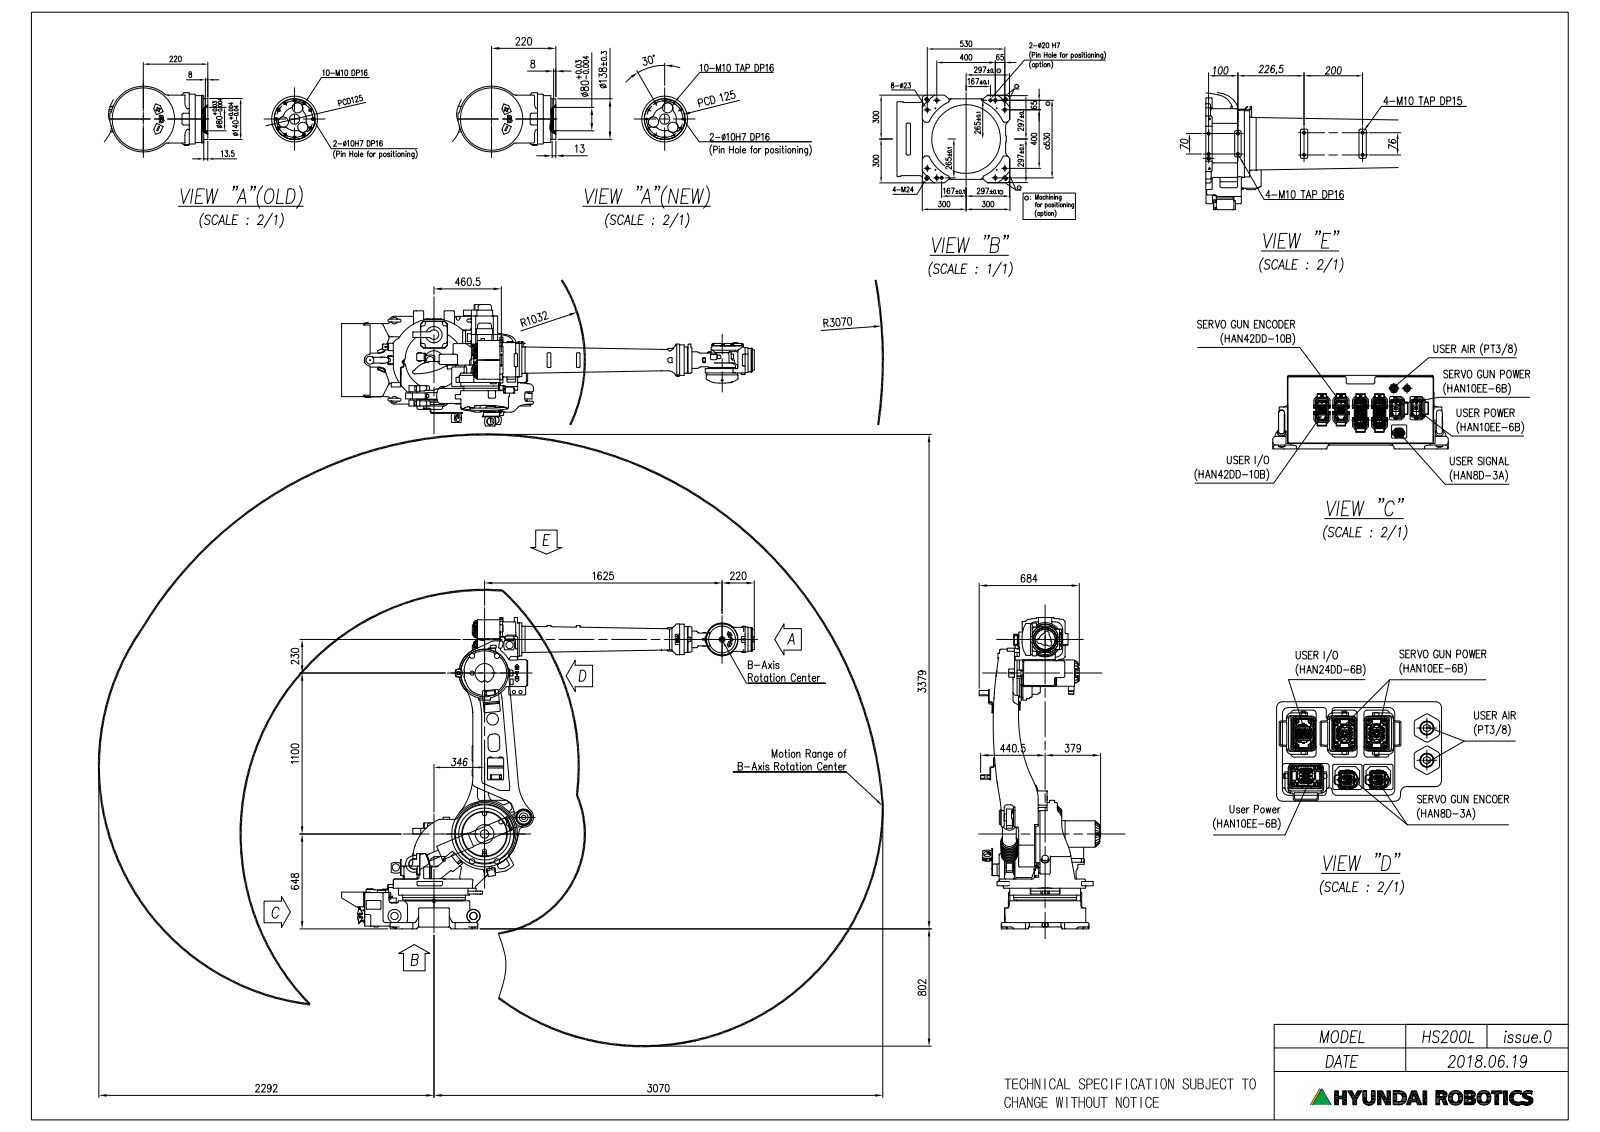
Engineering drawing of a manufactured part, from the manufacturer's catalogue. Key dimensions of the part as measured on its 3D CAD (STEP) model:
Part name (STEP PRODUCT): HS200L_LOWER FRAME HINGE; HS200L_GASKET; HS200L_ARM PIPE; HS200L (+8 more)
STEP written by: SolidWorks 2017 (AUTOMOTIVE_DESIGN)
Units: millimetres
Bodies: 43 solids, 3306 faces (1848 planar, 954 cylindrical, 504 other)
Overall size (bounding box): 2668.5 × 2138 × 734
Volume: 320 600 000 mm³ · Surface area: 11 850 000 mm²
Round holes (diameter × count): ⌀6 ×8, ⌀80 ×3, ⌀6.8 ×2, ⌀8 ×2, ⌀40 ×2, ⌀68 ×2, ⌀70 ×2, ⌀95 ×2, ⌀106 ×2, ⌀8.7 ×1, ⌀9.73 ×1, ⌀22 ×1
Round bosses / shafts (diameter × count): ⌀70 ×3, ⌀60 ×3, ⌀38.1 ×3, ⌀30 ×3, ⌀208 ×2, ⌀180 ×2, ⌀179 ×2, ⌀174.5 ×2
Partial cylindrical surfaces — rounded edges, fillets, slot ends (radius × count): R8 ×126, R10 ×36, R3 ×24, R5 ×23, R15 ×16, R6 ×12, R30 ×9, R20 ×8
Main face-to-face distances: 30, 173.1, 265, 91.9, 62.5, 235, 48, 170, 297.5, 25
Hole centre spacings: 68.54, 115.66, 130.82, 160.6, 10, 62.2, 65, 67.74
